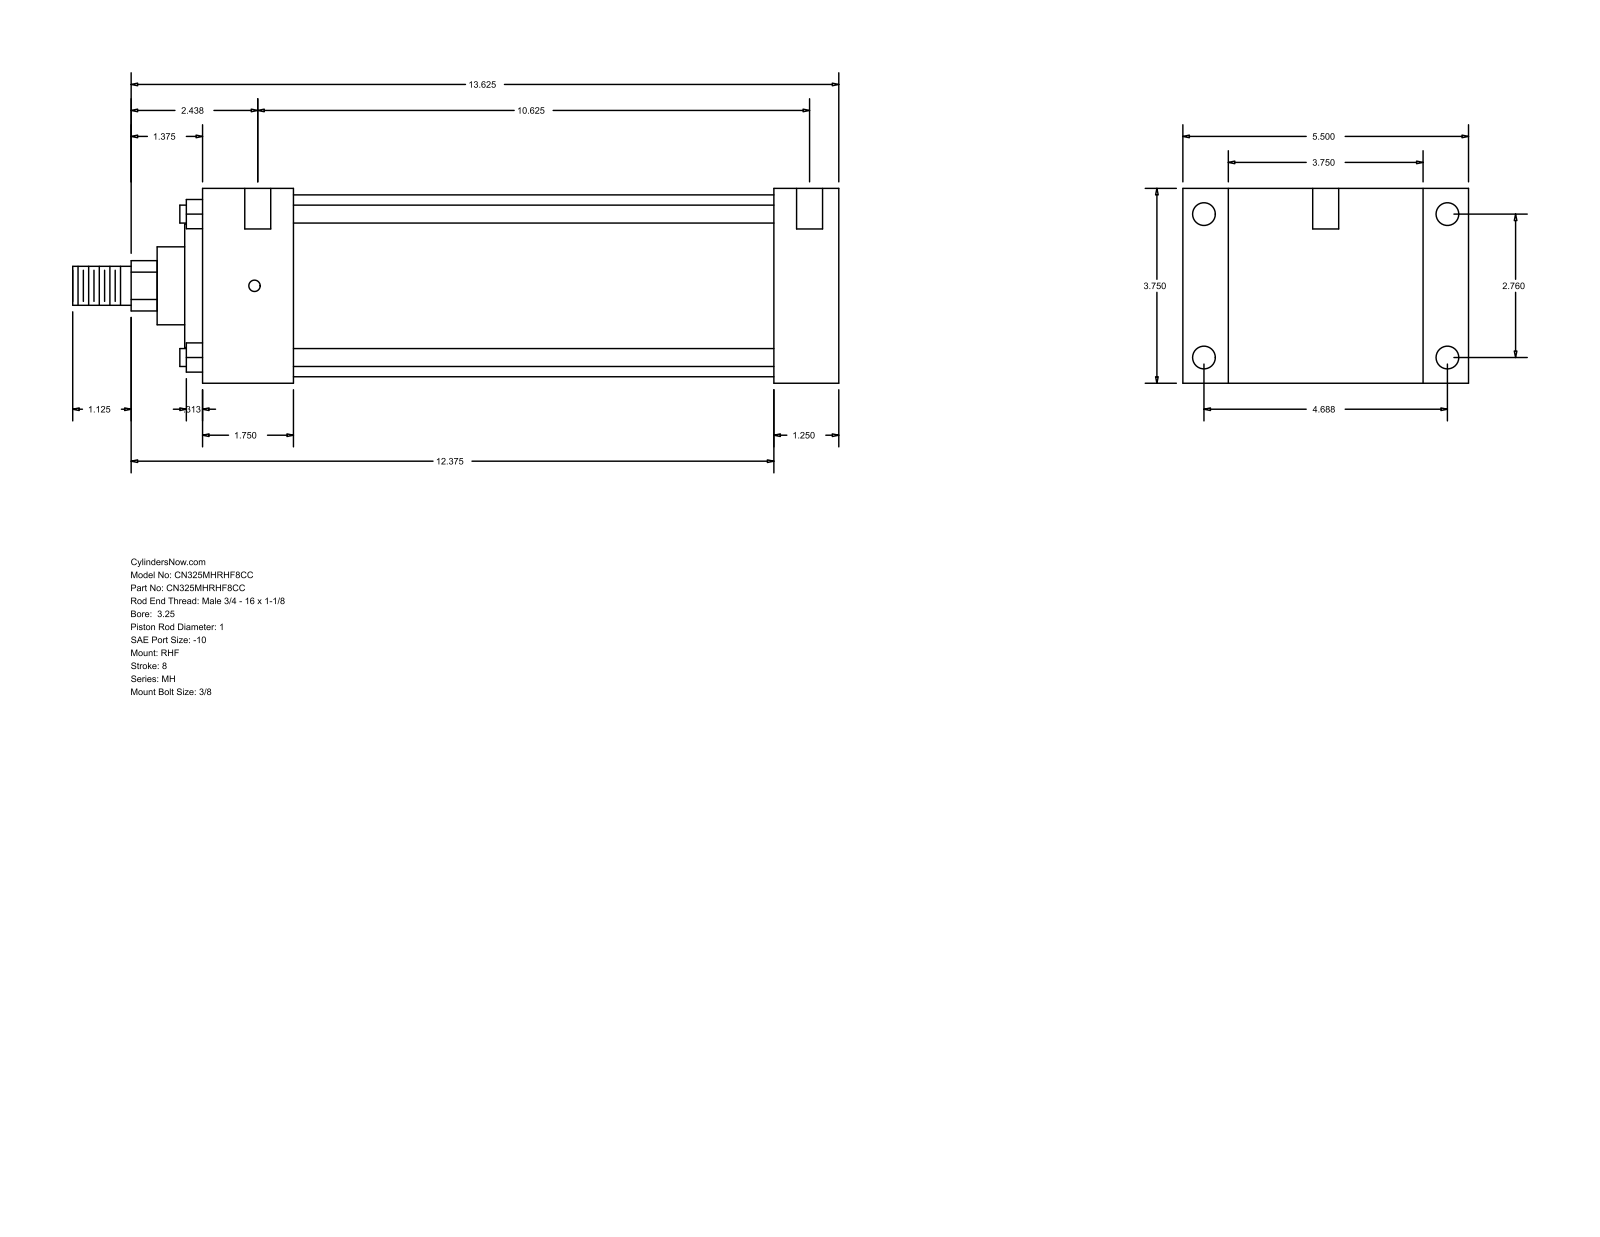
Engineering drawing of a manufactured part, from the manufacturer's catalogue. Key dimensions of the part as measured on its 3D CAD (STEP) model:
Part name (STEP PRODUCT): MH_RHF__0325_1
STEP written by: GSSL Pune (CONFIG_CONTROL_DESIGN)
Units: millimetres
Bodies: 0 solids, 90 faces (61 planar, 29 cylindrical, 0 other)
Overall size (bounding box): 374.65 × 139.7 × 95.25
Round holes (diameter × count): ⌀5.56 ×4, ⌀11.13 ×4, ⌀12.7 ×2
Round bosses / shafts (diameter × count): ⌀8.76 ×4, ⌀88.9 ×1, ⌀60.33 ×1, ⌀38.1 ×1, ⌀25.4 ×1, ⌀19.05 ×1
Partial cylindrical surfaces — rounded edges, fillets, slot ends (radius × count): R12.29 ×1
Main face-to-face distances: 95.24, 31.75, 22.23, 117.47, 279.4, 311.15, 139.7, 44.46, 234.94, 266.69
Hole centre spacings: 70.1, 119.06, 138.16, 276.22, 1.58, 4.76, 269.88, 271.46
